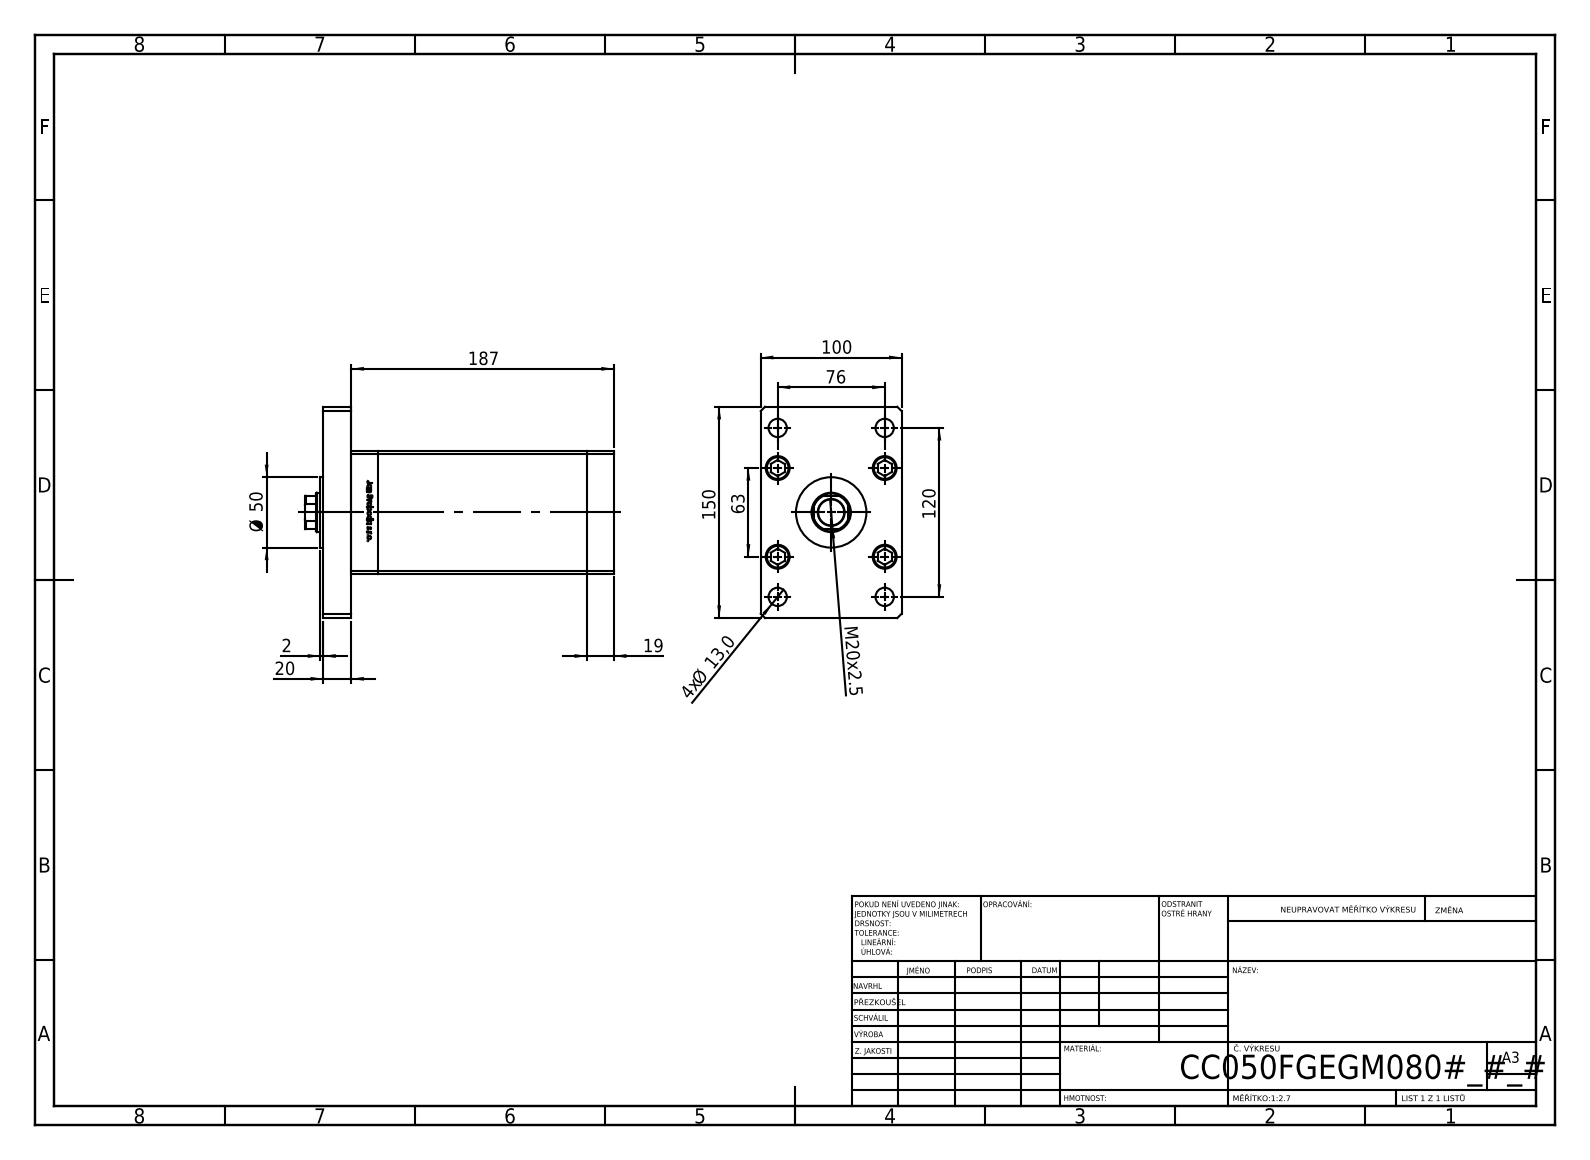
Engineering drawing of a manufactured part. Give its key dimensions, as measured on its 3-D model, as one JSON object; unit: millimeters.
{"part_name": "V220C_F_MIDDLE; V220C BACK_F; V220C_VC_F; ALLEN BOLT (+2 more)", "step_written_by": "SolidWorks 2019 (CONFIG_CONTROL_DESIGN)", "units": "millimeters", "bodies": {"solids": 19, "faces": 1311, "planar": 517, "cylindrical": 188, "other": 606}, "overall_size": [219.5, 150, 100], "volume_mm3": 1705000, "surface_area_mm2": 259381, "round_holes": [[13.5, 7], [18, 7], [12, 4], [13, 4], [17, 4], [2, 2], [13.16, 2], [18.5, 1], [28, 1], [29.5, 1]], "round_bosses_or_shafts": [[8, 9], [17, 5], [50, 1]], "partial_cylinders_radius": [[0.93, 2], [13.5, 1]], "face_to_face_distances": [19, 167.5, 100, 87, 20, 148.5, 39, 187.5, 186.5, 206.5], "hole_center_spacings": [34, 18.59, 28.5, 37.13, 39.64, 49.36, 57.95, 71.02]}
